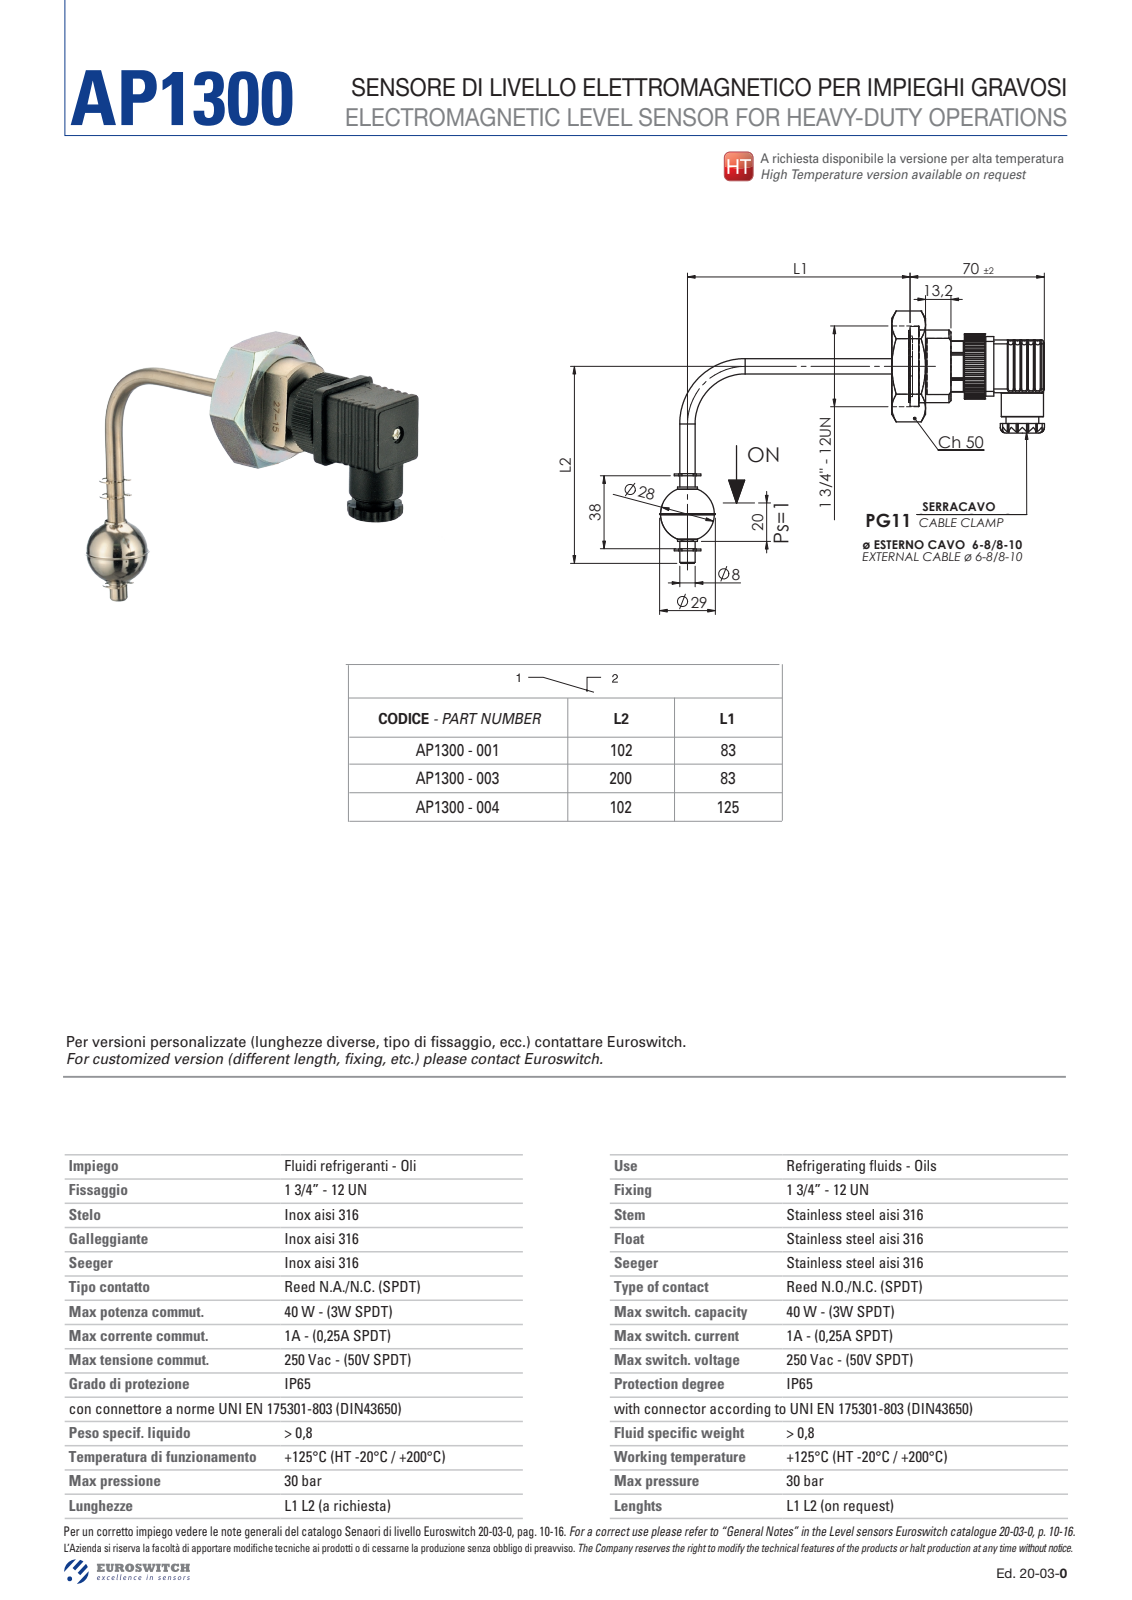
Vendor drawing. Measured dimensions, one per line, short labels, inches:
name: AP1300
written by: SolidWorks 2019 (AUTOMOTIVE_DESIGN)
unit: in
bodies: 0 solids, 673 faces (221 planar, 309 cylindrical, 143 other)
size: 8.275 × 5.162 × 2.101
holes: 1× ⌀0.276, 1× ⌀0.319, 1× ⌀0.366, 1× ⌀0.433, 1× ⌀1.24, 1× ⌀1.398, 1× ⌀1.496, 1× ⌀1.654
bosses: 2× ⌀0.315, 1× ⌀1.488, 1× ⌀1.142, 1× ⌀1.043, 1× ⌀0.862, 1× ⌀0.669, 1× ⌀0.406, 1× ⌀0.394
rounds: 36× R0.098, 25× R0.031, 14× R0.039, 12× R0.012, 8× R0.079, 6× R0.02, 4× R0.008, 2× R0.087
face distances: 1.969, 1.214, 0.268, 1.482, 0.374, 0.689, 0.421, 1.903, 0.694, 0.52
